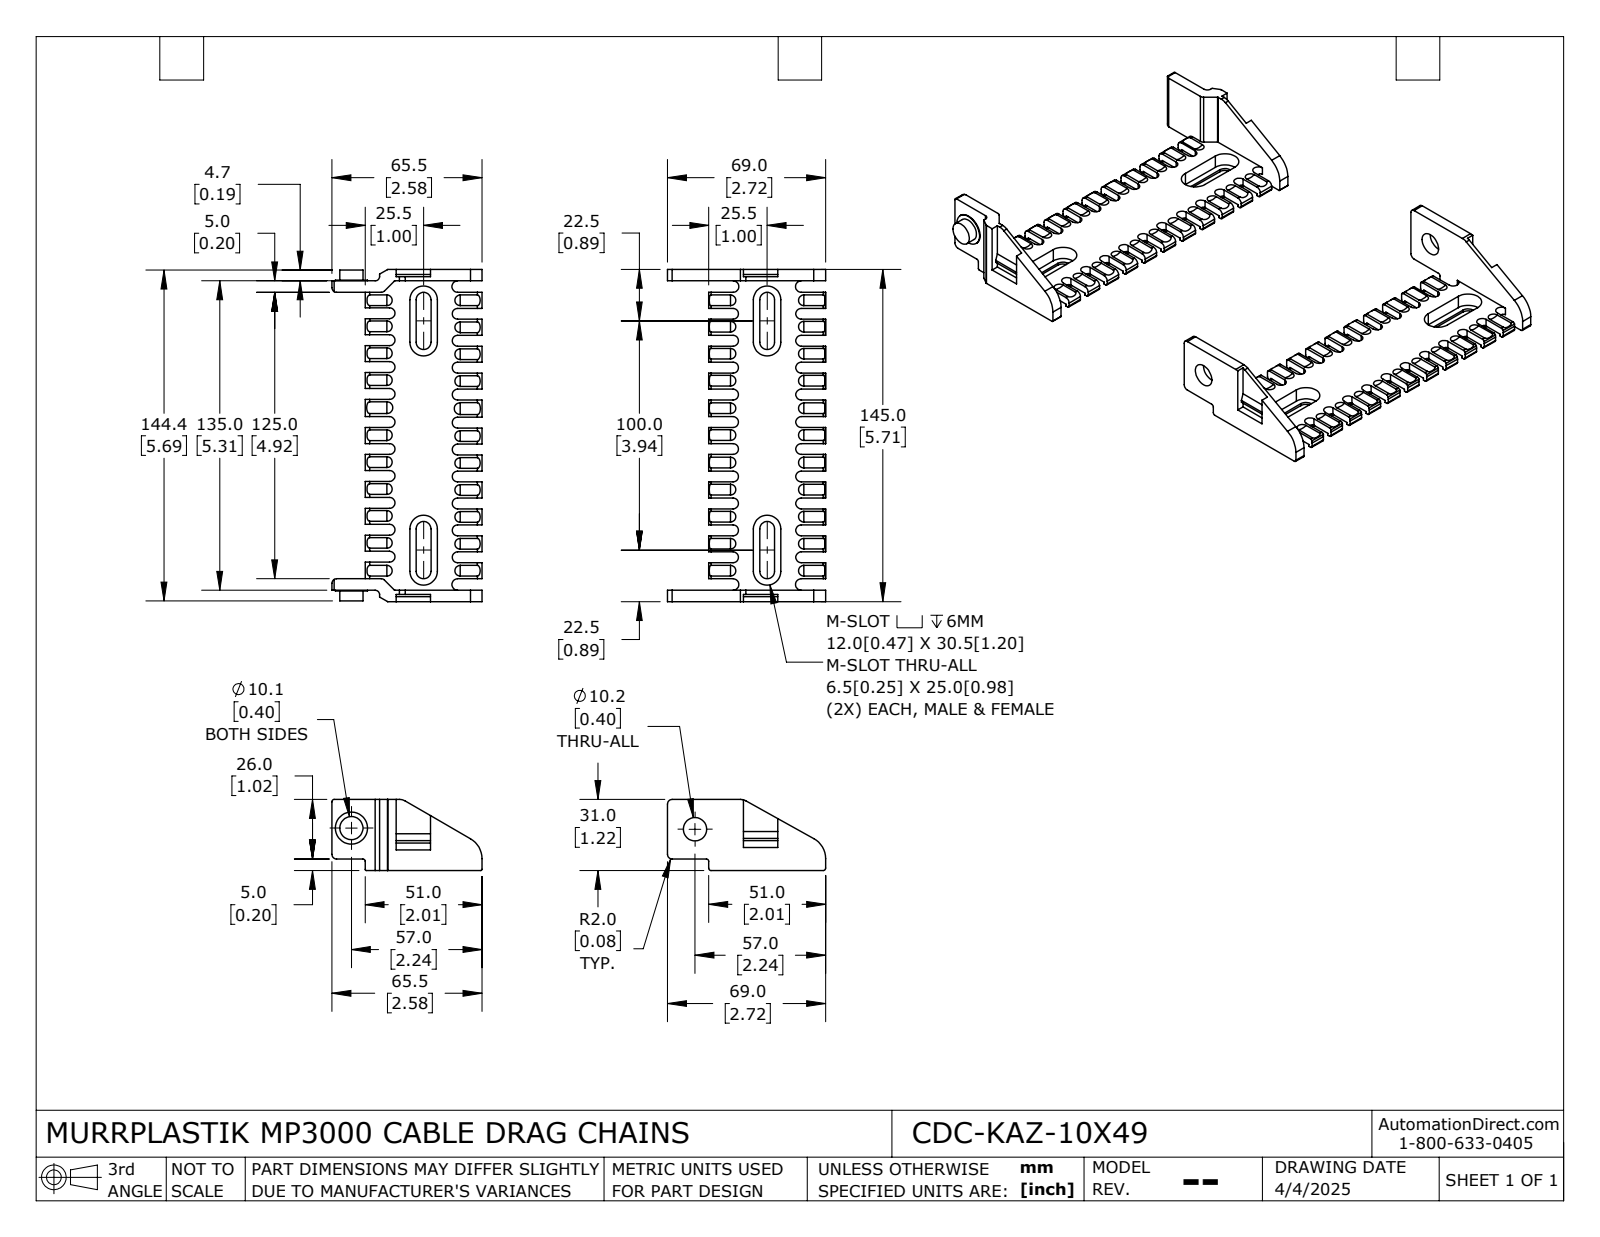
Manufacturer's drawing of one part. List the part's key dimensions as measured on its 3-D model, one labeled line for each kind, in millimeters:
Part name (STEP PRODUCT): CDC-KAZ-10X49
STEP written by: SolidWorks 2024 (AUTOMOTIVE_DESIGN)
Units: millimetres
Bodies: 2 solids, 757 faces (384 planar, 329 cylindrical, 44 other)
Overall size (bounding box): 215.5 × 145 × 31
Volume: 83 833 mm³ · Surface area: 46 817 mm²
Round holes (diameter × count): ⌀10.2 ×1
Round bosses / shafts (diameter × count): ⌀14 ×1, ⌀10.1 ×1
Partial cylindrical surfaces — rounded edges, fillets, slot ends (radius × count): R2.38 ×40, R7 ×29, R1 ×15, R2 ×13, R3.25 ×8, R6 ×8, R2.5 ×6, R0.5 ×4
Main face-to-face distances: 7, 5, 3.5, 140, 135, 145, 10, 130, 2.5, 1
